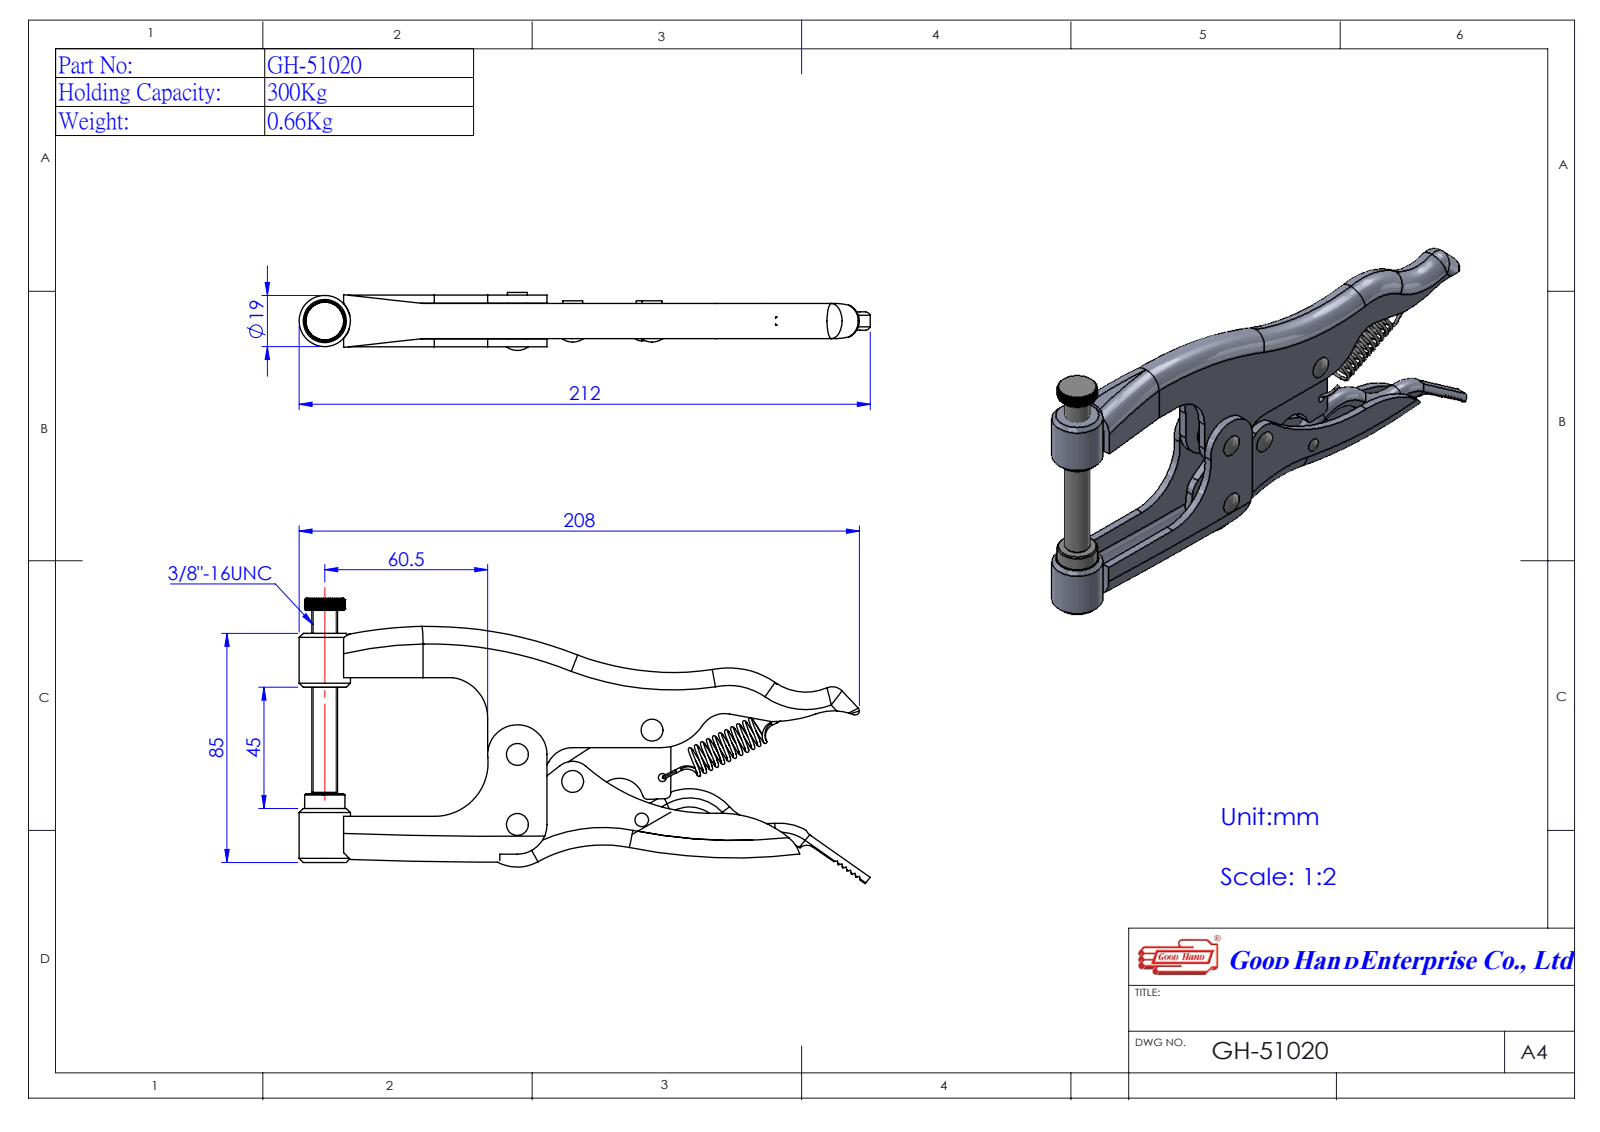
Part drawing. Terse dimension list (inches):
name: GH-51020(單一)-2; Group1^GH-51020(單一)-2
written by: SolidWorks 2016 (AUTOMOTIVE_DESIGN)
unit: in
bodies: 1 solid, 563 faces (198 planar, 154 cylindrical, 211 other)
size: 8.346 × 4.168 × 0.846
volume: 5.062 in³; area: 81.59 in²
bosses: 4× ⌀0.291, 4× ⌀0.252, 3× ⌀0.047, 2× ⌀0.197, 1× ⌀0.748, 1× ⌀0.591, 1× ⌀0.375, 1× ⌀0.157
rounds: 3× R0.256, 2× R0.059, 2× R0.079, 2× R0.138, 2× R0.276, 2× R0.295, 2× R0.394, 2× R0.433
face distances: 0.118, 0.394, 0.122, 0.516, 0.276, 0.512, 0.398, 0.24, 0.634, 0.638
